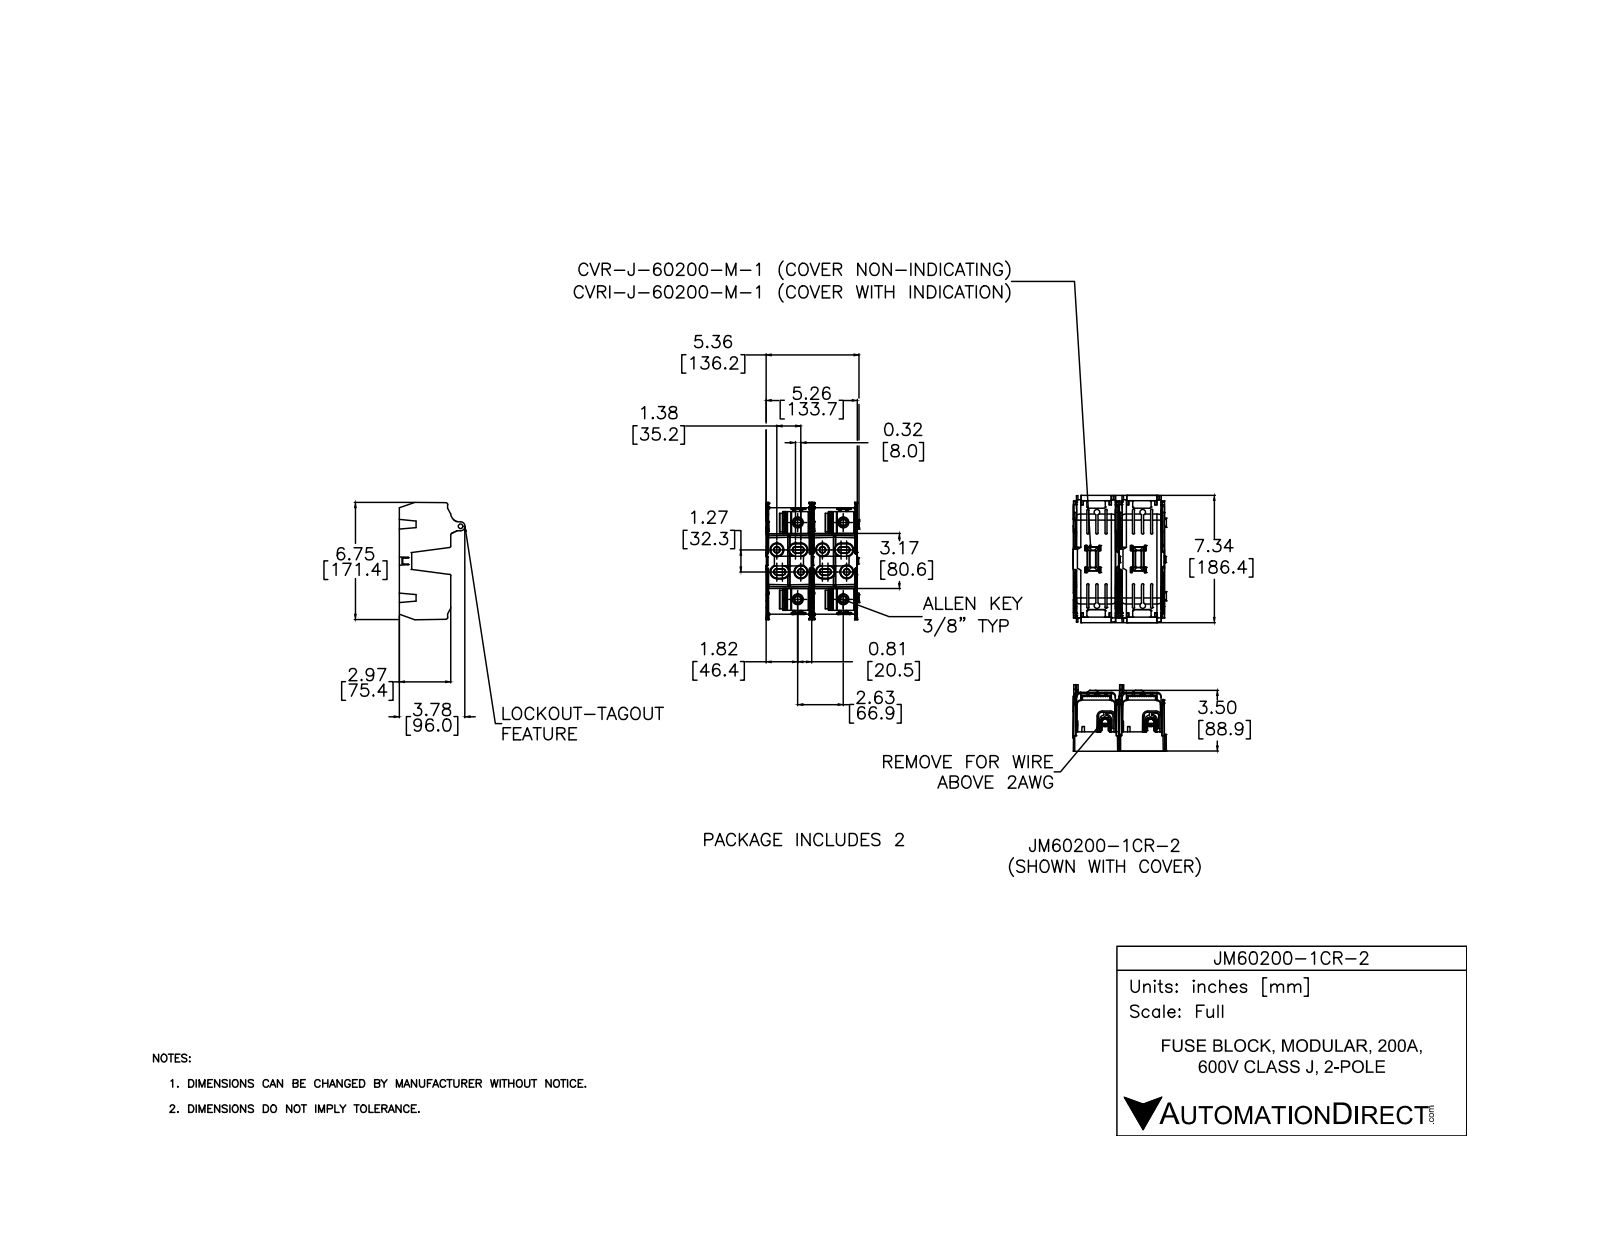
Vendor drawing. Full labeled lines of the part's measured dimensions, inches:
Part name (STEP PRODUCT): JM60200-1CR-2
STEP written by: SolidWorks 2021 (CONFIG_CONTROL_DESIGN)
Units: inches
Bodies: 0 solids, 1634 faces (482 planar, 688 cylindrical, 464 other)
Overall size (bounding box): 6.757 × 5.362 × 3.779
Round bosses / shafts (diameter × count): ⌀0.197 ×8, ⌀0.625 ×6, ⌀0.406 ×2, ⌀0.04 ×2, ⌀0.277 ×1
Partial cylindrical surfaces — rounded edges, fillets, slot ends (radius × count): R0.02 ×190, R0.01 ×84, R0.01 ×56, R0.01 ×20, R0.079 ×19, R0.015 ×10, R0.119 ×10, R0.02 ×8
Main face-to-face distances: 2.631, 2.502, 2.503, 1.108, 0.129, 5.133, 0.048, 5.134, 0.128, 0.032
